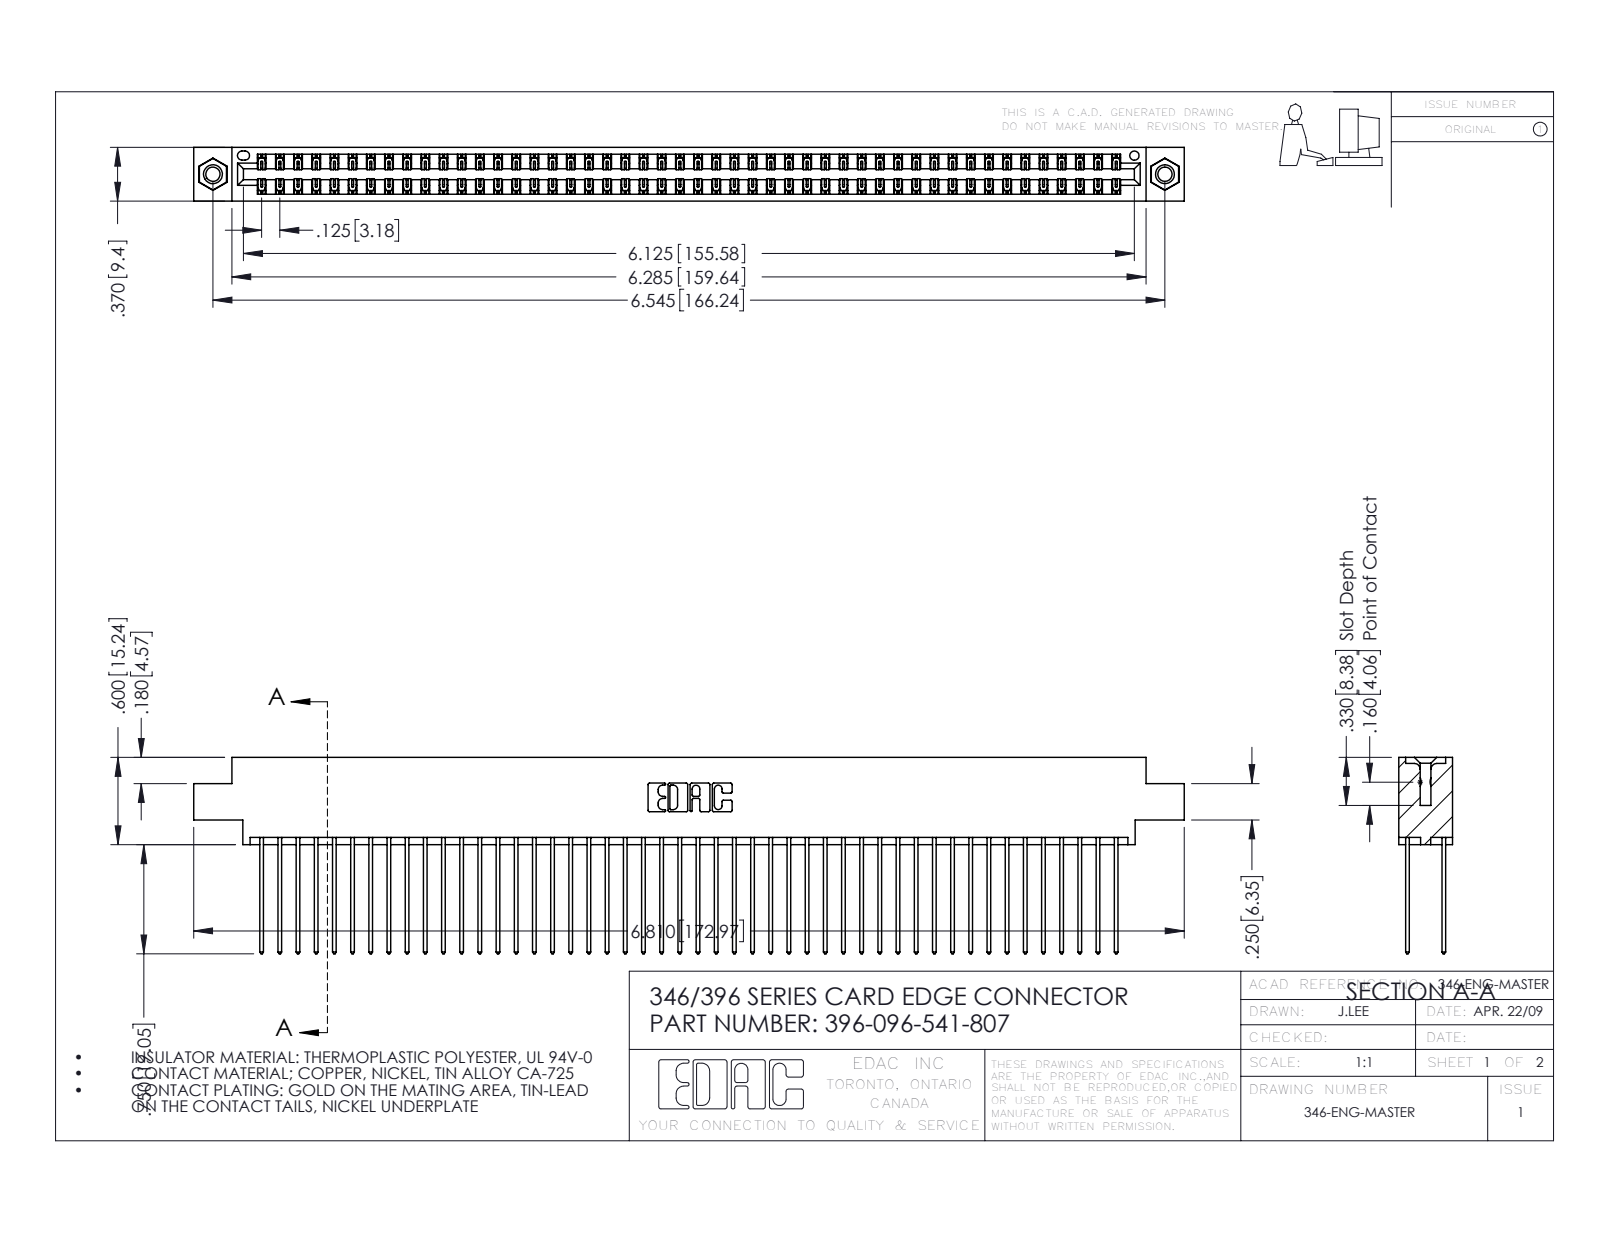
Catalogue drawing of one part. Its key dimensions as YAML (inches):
part_name: "346 Part_0.170 Offset - 0.156 Dia-TI; 396-096-541-807; 345-250-001_345-250-005-103; 345-292-001_345-293-141"
step_written_by: "SolidWorks 2016 (CONFIG_CONTROL_DESIGN)"
units: inches
bodies: {solids: 99, faces: 5178, planar: 3472, cylindrical: 1690, other: 16}
overall_size: [6.81, 1.35, 0.37]
volume: 1.055
surface_area: 41.42
round_holes:
  - {diameter: 0.098, count: 2}
  - {diameter: 0.125, count: 2}
  - {diameter: 0.156, count: 2}
  - {diameter: 0.064, count: 1}
round_bosses_or_shafts:
  - {diameter: 0.155, count: 2}
partial_cylinders:
  - {radius: 0.006, count: 144}
  - {radius: 0.01, count: 96}
  - {radius: 0.01, count: 22}
  - {radius: 0.007, count: 6}
  - {radius: 0.031, count: 6}
  - {radius: 0.026, count: 3}
  - {radius: 0.014, count: 2}
  - {radius: 0.022, count: 2}
face_to_face_distances: [0.048, 0.322, 0.25, 0.072, 0.298, 0.025, 0.37, 0.275, 0.225, 0.222]
hole_center_spacings: [0.246, 6.336, 6.545]
